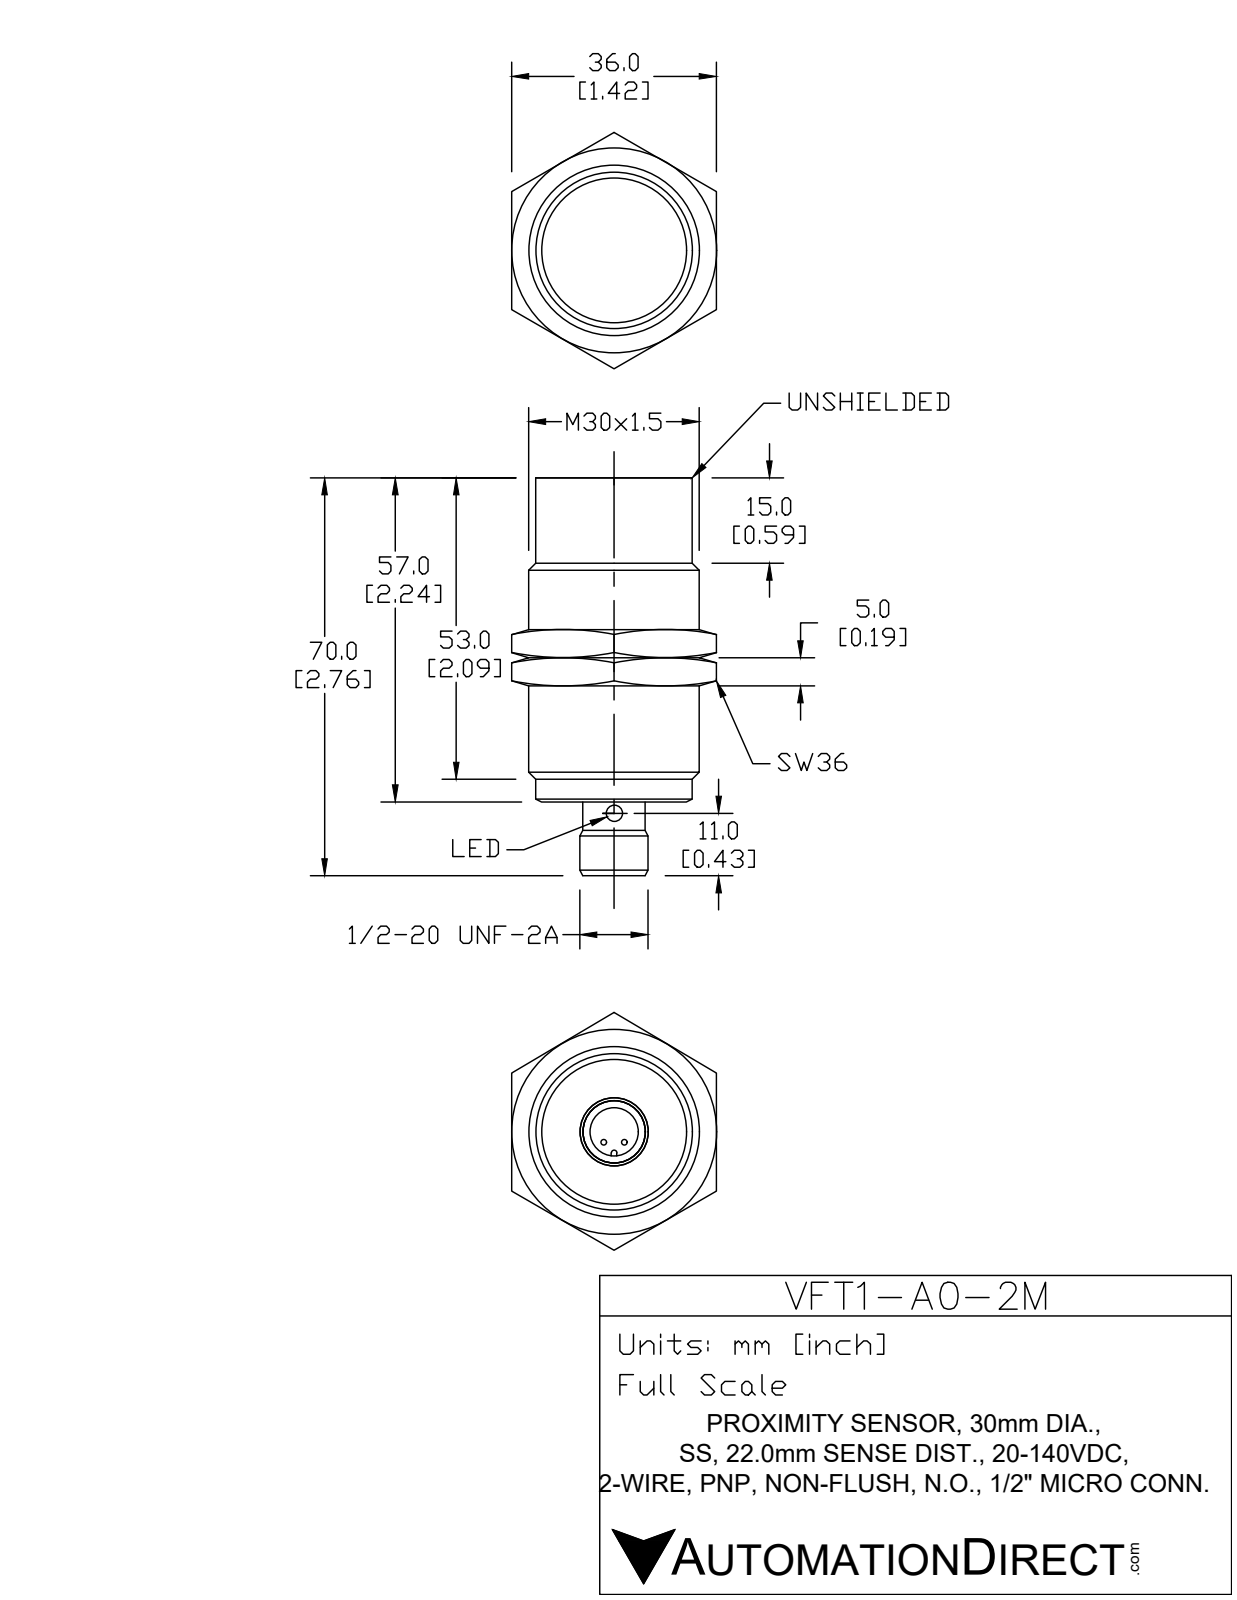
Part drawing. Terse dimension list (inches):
name: VFT1-A0-2M
written by: SolidWorks 2017 (AUTOMOTIVE_DESIGN)
unit: in
bodies: 3 solids, 99 faces (24 planar, 31 cylindrical, 44 other)
size: 2.756 × 1.637 × 1.417
volume: 2.681 in³; area: 17.26 in²
holes: 2× ⌀0.098, 1× ⌀0.331, 1× ⌀1.117
bosses: 1× ⌀1.181, 1× ⌀1.094, 1× ⌀0.5, 1× ⌀0.417
rounds: 1× R0.195
face distances: 0.197, 1.575, 1.417, 0.669, 2.244, 1.378, 0.472, 0.866, 0.394, 1.772
